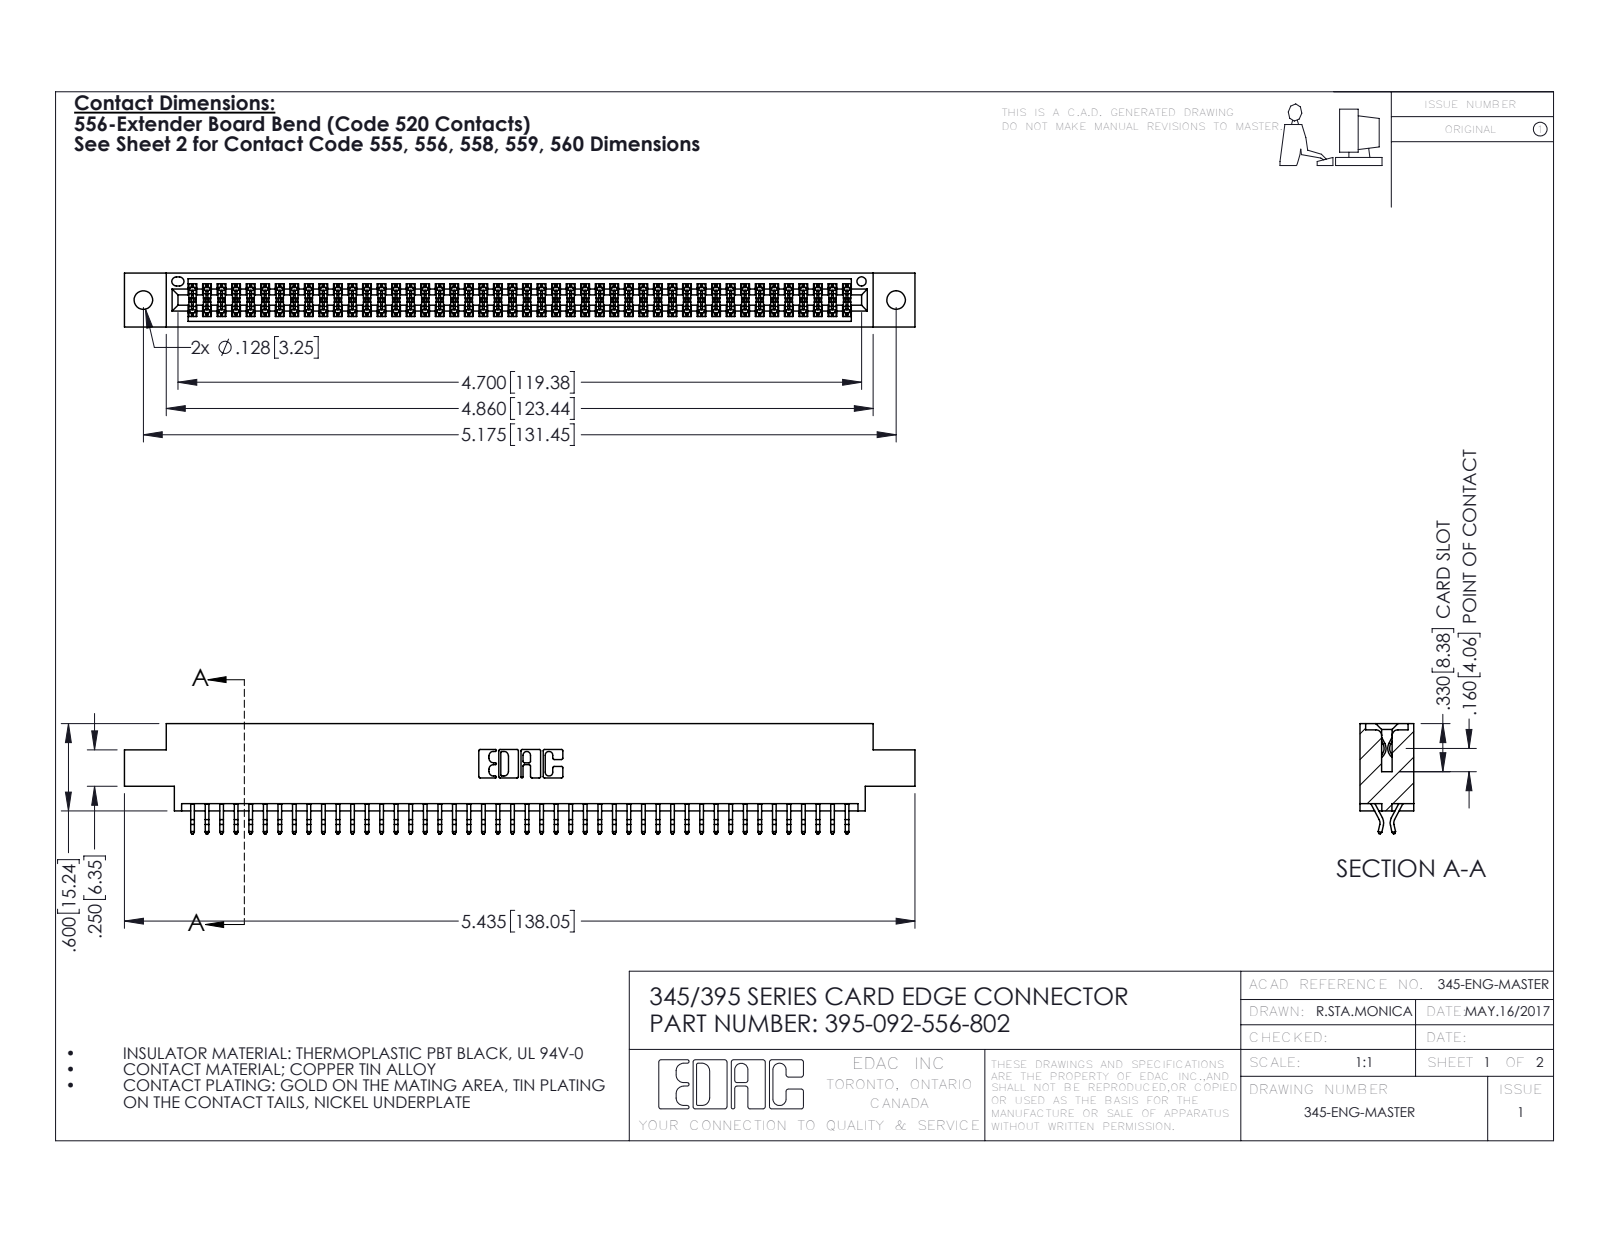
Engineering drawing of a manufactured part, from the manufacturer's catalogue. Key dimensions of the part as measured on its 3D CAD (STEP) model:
Part name (STEP PRODUCT): 345-292-001_556 Tail; 345 Part_0.170 Offset - 0.128 Dia; 395-092-556-802
STEP written by: SolidWorks 2016 (CONFIG_CONTROL_DESIGN)
Units: inches
Bodies: 93 solids, 5282 faces (3488 planar, 1794 cylindrical, 0 other)
Overall size (bounding box): 5.435 × 0.757 × 0.37
Volume: 0.811 in³ · Surface area: 30.25 in²
Round holes (diameter × count): ⌀0.128 ×2, ⌀0.064 ×1
Partial cylindrical surfaces — rounded edges, fillets, slot ends (radius × count): R0.006 ×138, R0.01 ×22, R0.007 ×6, R0.031 ×6, R0.026 ×3, R0.01 ×2, R0.014 ×2, R0.019 ×2
Main face-to-face distances: 0.298, 0.072, 0.37, 0.2, 0.025, 0.098, 0.272, 0.225, 0.175, 0.149
Hole centre spacings: 0.27, 4.939, 5.175
